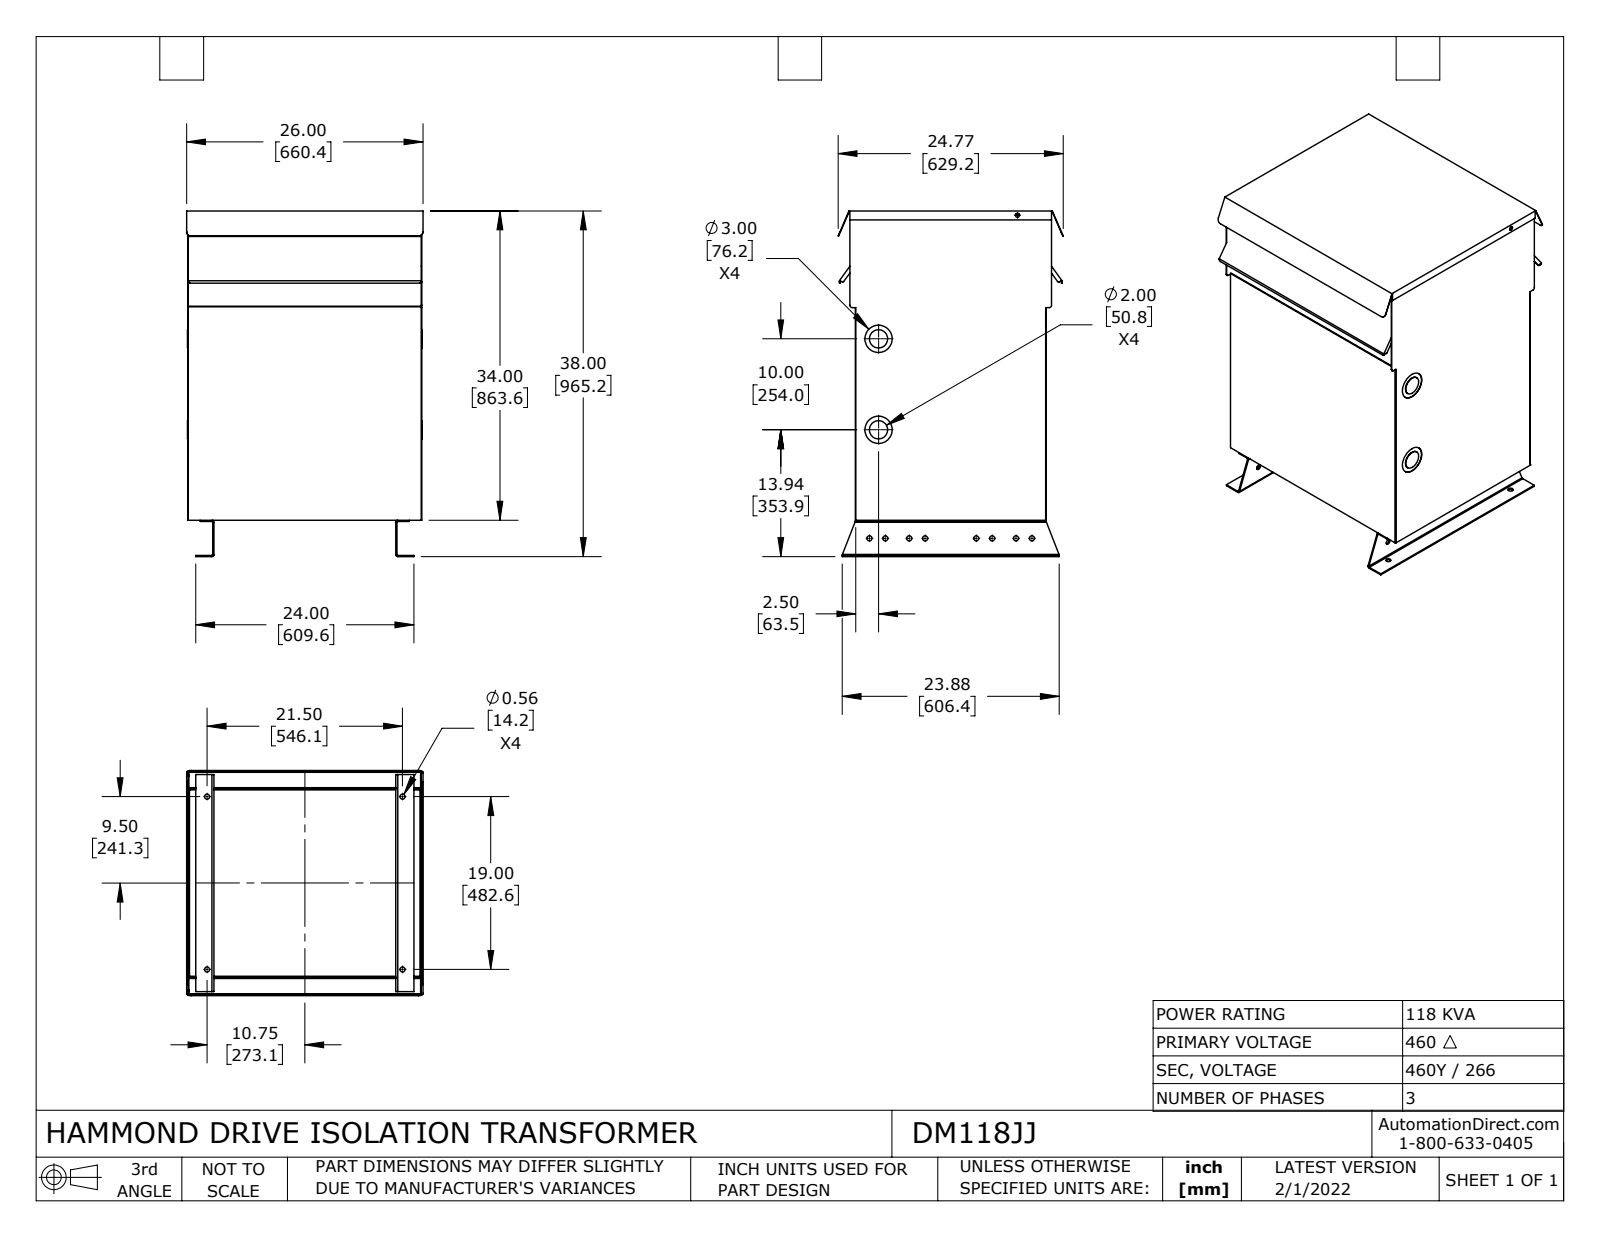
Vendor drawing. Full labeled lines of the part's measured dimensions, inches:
Part name (STEP PRODUCT): DM118JJ
STEP written by: SolidWorks 2021 (CONFIG_CONTROL_DESIGN)
Units: inches
Bodies: 10 solids, 299 faces (172 planar, 127 cylindrical, 0 other)
Overall size (bounding box): 38 × 26 × 24.773
Volume: 363.5 in³ · Surface area: 10 897 in²
Round holes (diameter × count): ⌀0.563 ×8, ⌀0.56 ×4, ⌀0.438 ×2, ⌀3 ×2, ⌀0.44 ×1
Round bosses / shafts (diameter × count): ⌀2 ×2
Partial cylindrical surfaces — rounded edges, fillets, slot ends (radius × count): R0.06 ×6, R0.135 ×6, R0.06 ×4, R0.09 ×4, R0.12 ×4, R0.125 ×4, R0.224 ×4, R0.5 ×4
Main face-to-face distances: 0.06, 25.68, 20.935, 20.875, 25.74, 25.62, 0.075, 20.994, 34, 33.94
Hole centre spacings: 1.75, 4.375, 11.75, 10, 2.625, 6.125, 7.375, 13.5
